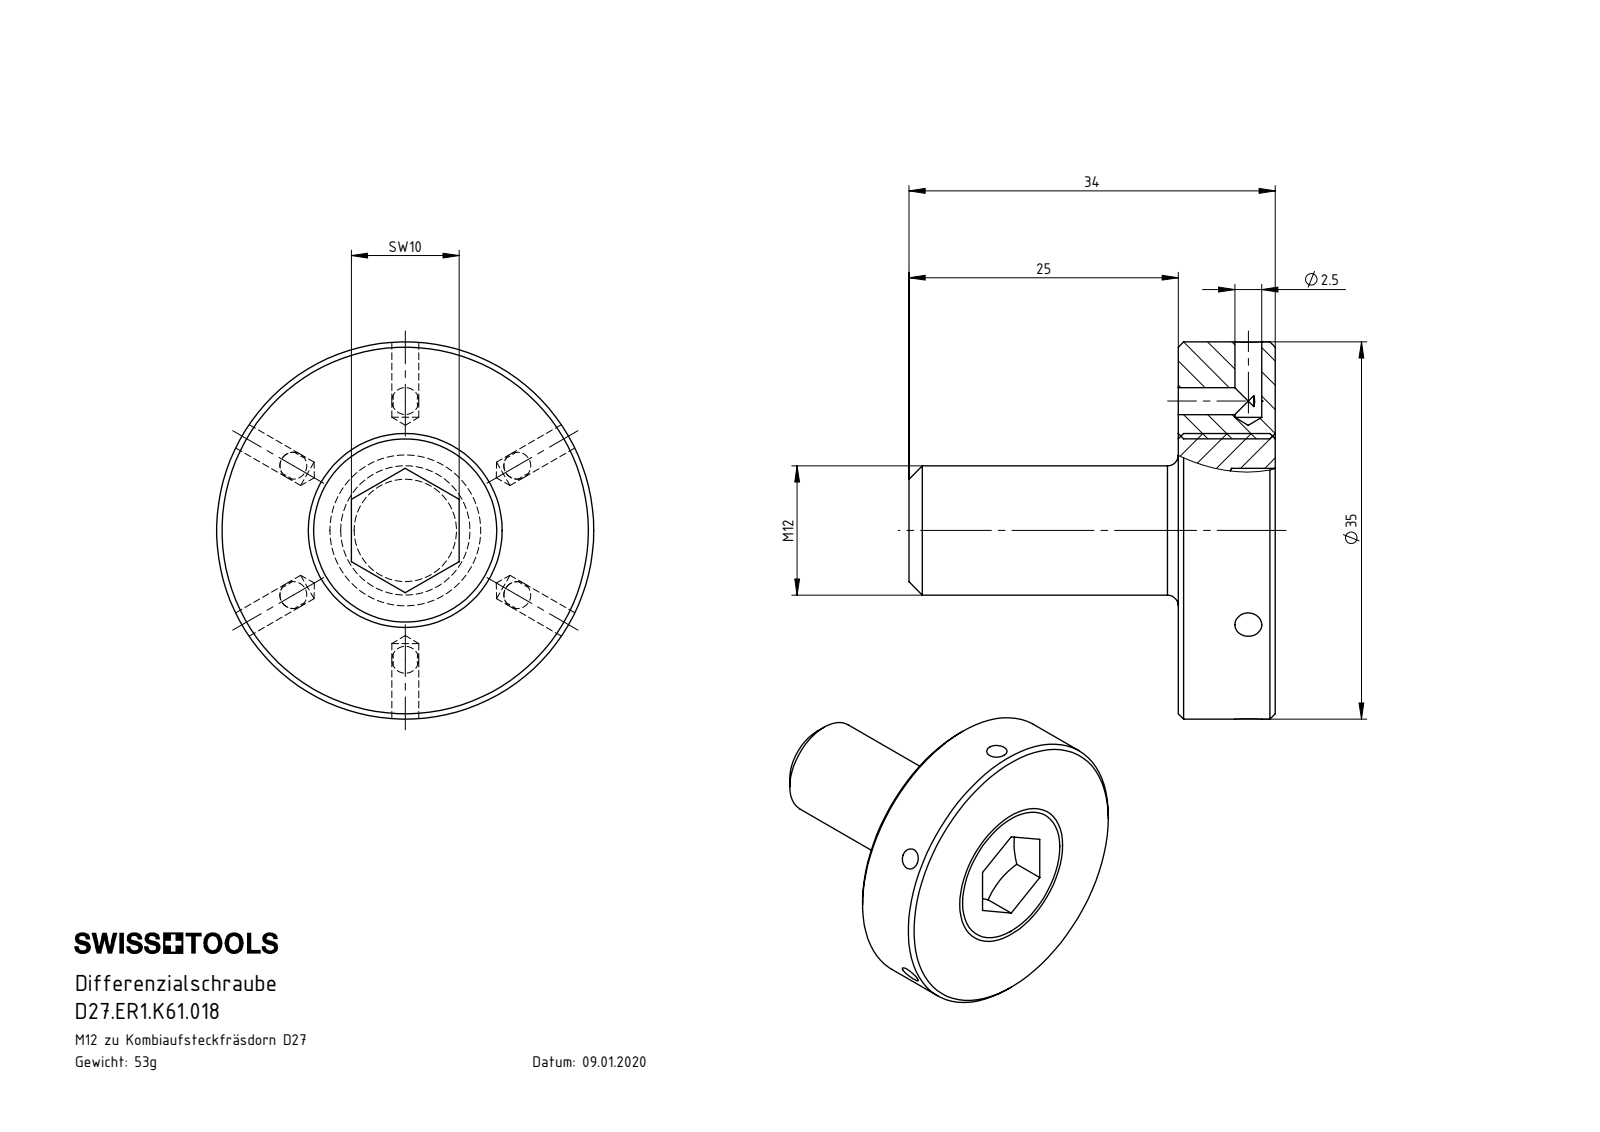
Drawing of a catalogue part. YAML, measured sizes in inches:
part_name: "D27-ER1.K61.018; D27-ER1.K62.009_A; D27-ER1.K63.018_A"
step_written_by: "SolidWorks 2012 (AUTOMOTIVE_DESIGN)"
units: inches
bodies: {solids: 2, faces: 119, planar: 11, cylindrical: 52, other: 56}
overall_size: [1.378, 1.378, 1.339]
volume: 0.66
surface_area: 8.412
round_holes:
  - {diameter: 0.098, count: 9}
  - {diameter: 0.669, count: 1}
round_bosses_or_shafts:
  - {diameter: 1.378, count: 1}
  - {diameter: 0.709, count: 1}
  - {diameter: 0.472, count: 1}
face_to_face_distances: [0.354, 0.394, 0.984, 1.339]
hole_center_spacings: [0.472, 0.818, 0.945]
